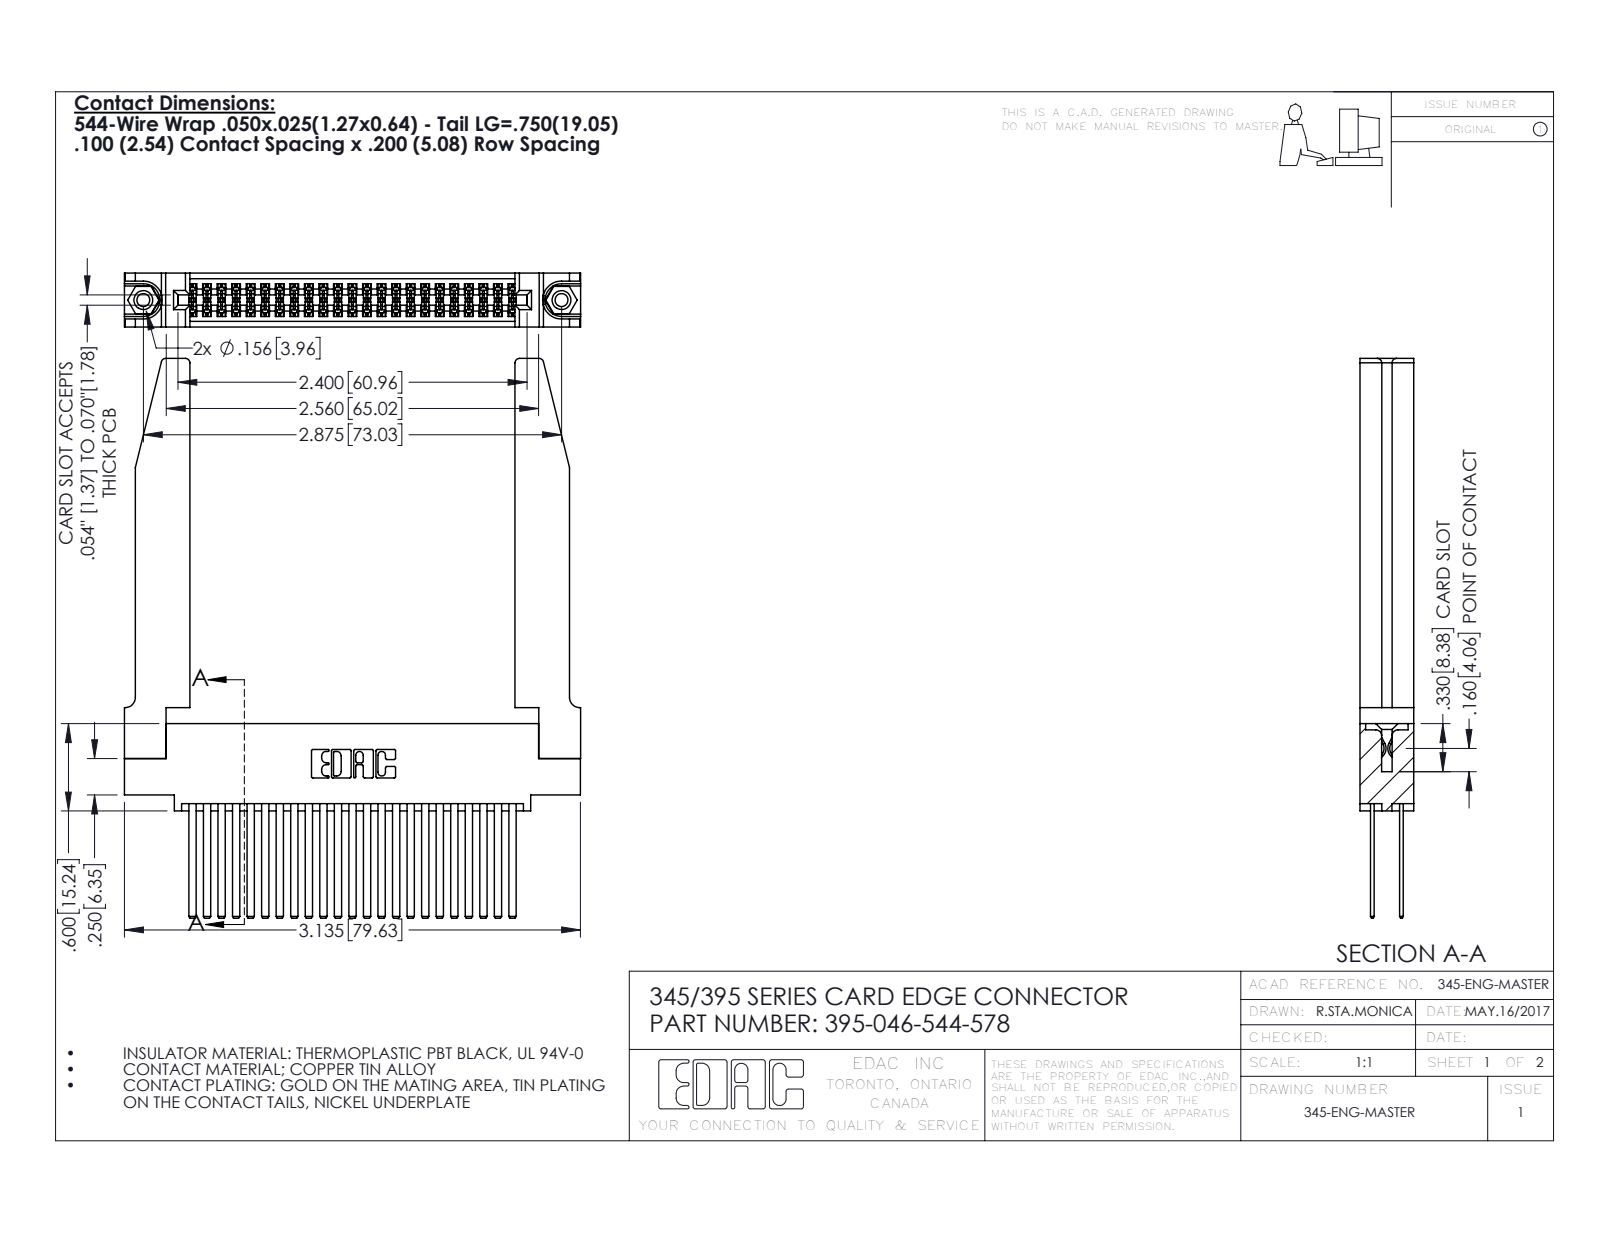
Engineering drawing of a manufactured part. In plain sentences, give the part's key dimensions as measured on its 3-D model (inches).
The part is named "345-220-078_345-220-078; 345-292-001_345-293-144; 395-046-544-578; 345-250-001_345-250-001-102 (+1 more)". Its 3-D file was written by "SolidWorks 2016 (CONFIG_CONTROL_DESIGN)". It is 51 solids with 2388 faces: 1560 planar, 776 cylindrical and 52 other. Overall it measures 3.847 by 3.136 by 0.37 inches. Its volume is 0.97 cubic inches and its surface area 31.74 square inches. Round holes: 2 of diameter 0.089, 2 of diameter 0.125, 2 of diameter 0.156, 1 of diameter 0.064. Round bosses or shafts: 2 of diameter 0.155. Partial cylindrical surfaces (rounded edges, fillets, slot ends): 69 of radius 0.006, 22 of radius 0.01, 8 of radius 0.03, 6 of radius 0.007, 6 of radius 0.031, 3 of radius 0.026, 2 of radius 0.014, 2 of radius 0.019. The main face-to-face distances are 0.072, 0.298, 0.37, 0.098, 0.272, 0.025, 0.2, 0.225, 0.175, 0.148. The hole center spacings are 0.27, 2.641, 2.875.
